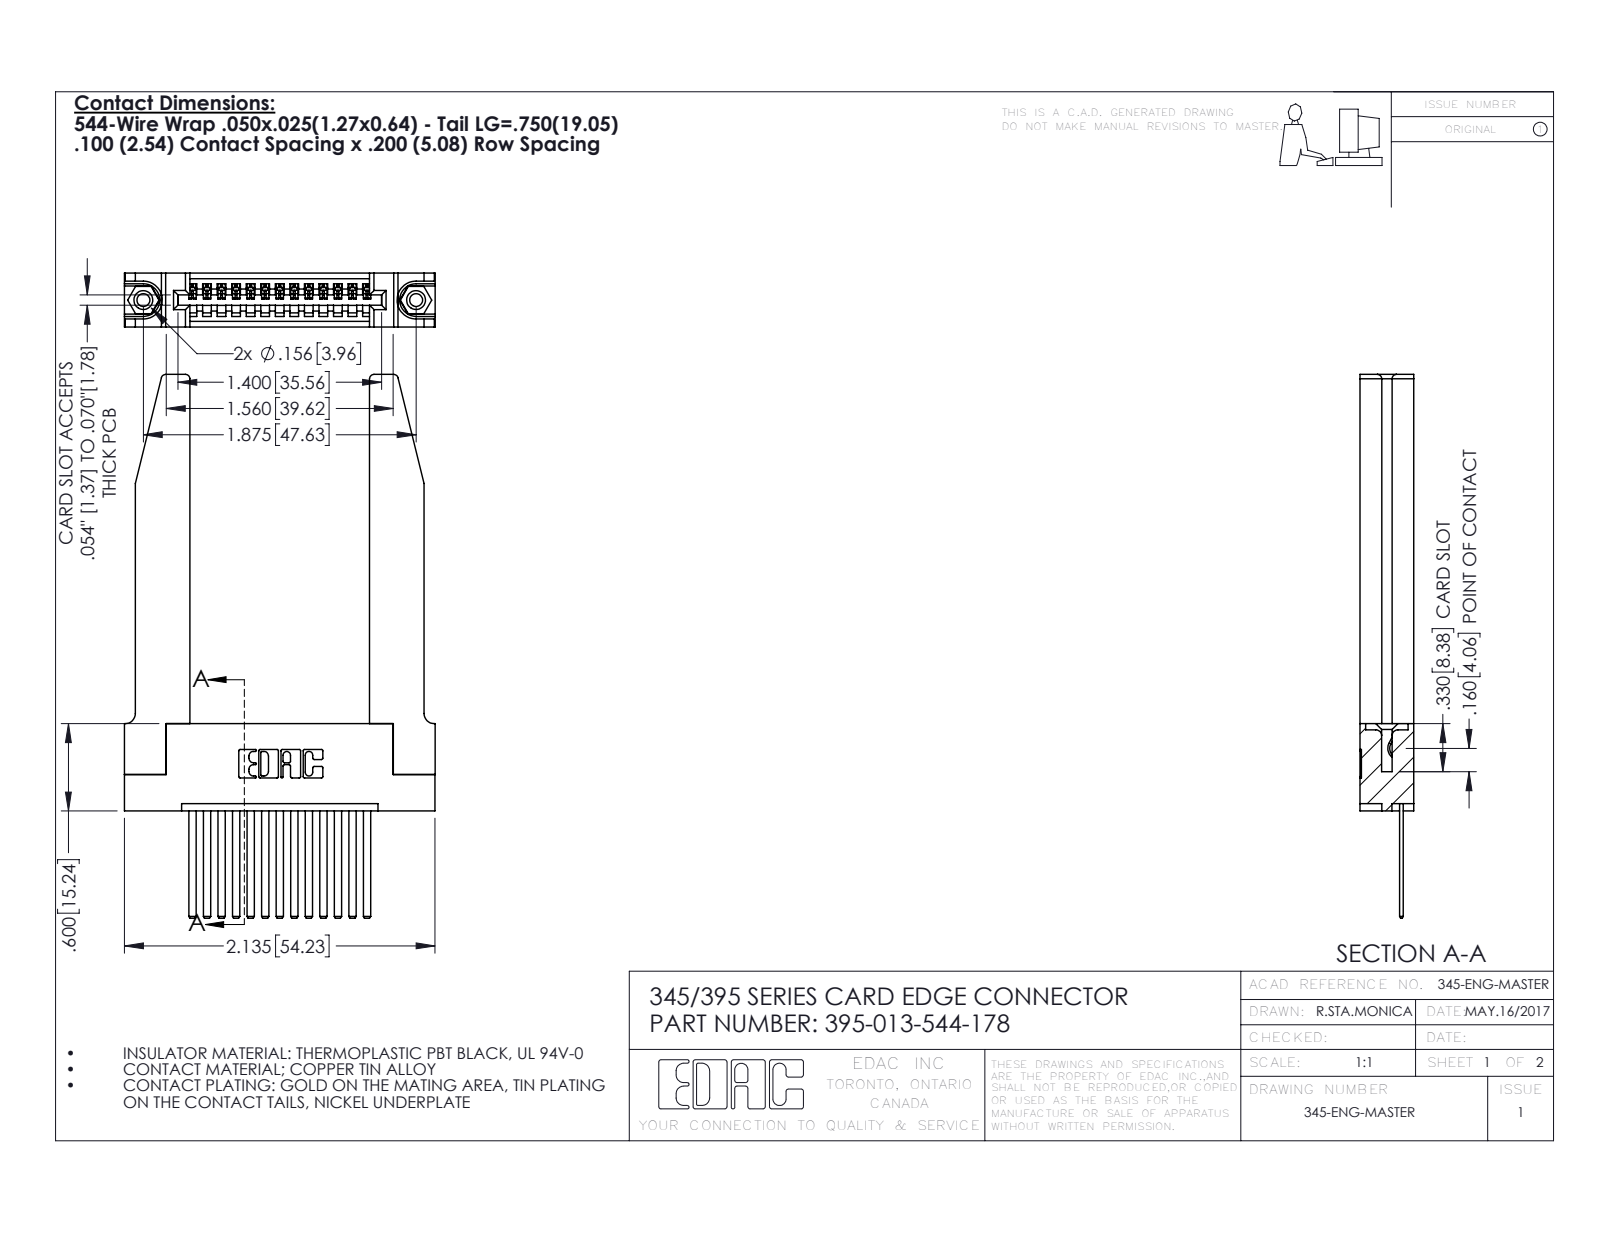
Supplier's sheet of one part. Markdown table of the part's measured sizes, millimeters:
| quantity | value |
| --- | --- |
| part name | 395-013-544-178; 345-250-001_345-250-001-102; 345-220-078_345-220-078; 345-292-001_345-293-144 (+1 more) |
| STEP written by | SolidWorks 2016 (CONFIG_CONTROL_DESIGN) |
| units | millimeters |
| bodies | 18 solids, 1036 faces (690 planar, 294 cylindrical, 52 other) |
| overall size | 94.9 × 54.3 × 9.4 |
| volume | 12 800 mm³ |
| surface area | 13 640 mm² |
| round holes (diameter × count) | 2.3 × 2, 3.2 × 2, 4 × 2, 1.6 × 1 |
| round bosses / shafts (diameter × count) | 3.9 × 2 |
| partial cylindrical surfaces (radius × count) | 0.2 × 26, 0.3 × 22, 0.8 × 8, 0.2 × 6, 0.8 × 6, 0.7 × 3, 0.8 × 2, 1 × 2 |
| main face-to-face distances | 9.4, 1.8, 7.6, 5.1, 2.5, 6.9, 0.6, 3.8, 3.8, 2 |
| hole center spacings | 6.9, 41.7, 47.6 |
